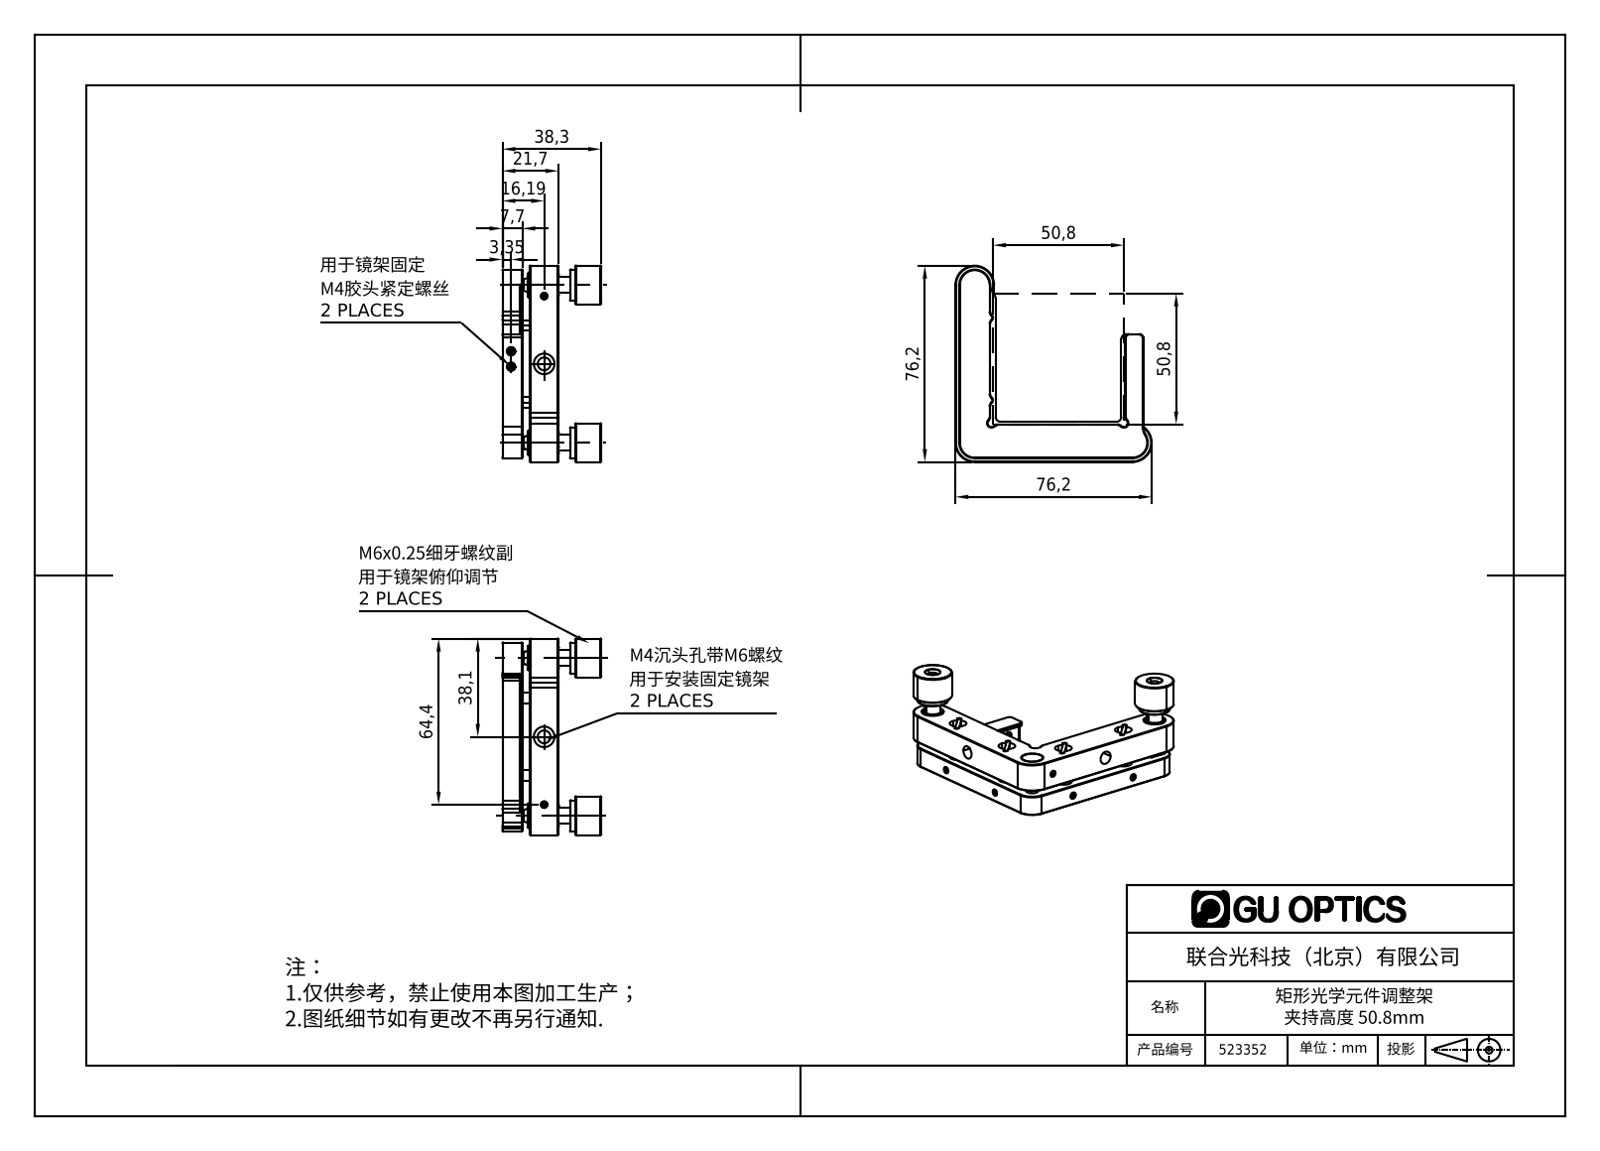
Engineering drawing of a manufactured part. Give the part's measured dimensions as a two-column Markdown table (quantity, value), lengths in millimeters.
| quantity | value |
| --- | --- |
| part name | 523352 |
| STEP written by | SolidWorks 2020 (CONFIG_CONTROL_DESIGN) |
| units | millimeters |
| bodies | 0 solids, 423 faces (157 planar, 119 cylindrical, 147 other) |
| overall size | 76.2 × 76.2 × 38.3 |
| round holes (diameter × count) | 6.5 × 4, 8.6 × 3, 9.5 × 3, 4 × 2, 5 × 2, 8 × 2, 2.5 × 1 |
| round bosses / shafts (diameter × count) | 1.5 × 6, 4 × 4, 15 × 2, 12 × 2, 6 × 2, 3.3 × 2, 2 × 2 |
| partial cylindrical surfaces (radius × count) | 2 × 12, 0.8 × 8, 1.5 × 4, 3 × 3, 1.25 × 2, 6 × 2, 5 × 1, 7.5 × 1 |
| main face-to-face distances | 7.7, 13.99, 21.69, 11, 10.69, 2.99, 1.5, 13.5, 15, 12 |
| hole center spacings | 15.6, 45.6, 30, 48.19, 61.2, 63.16, 76.32, 22.06 |
